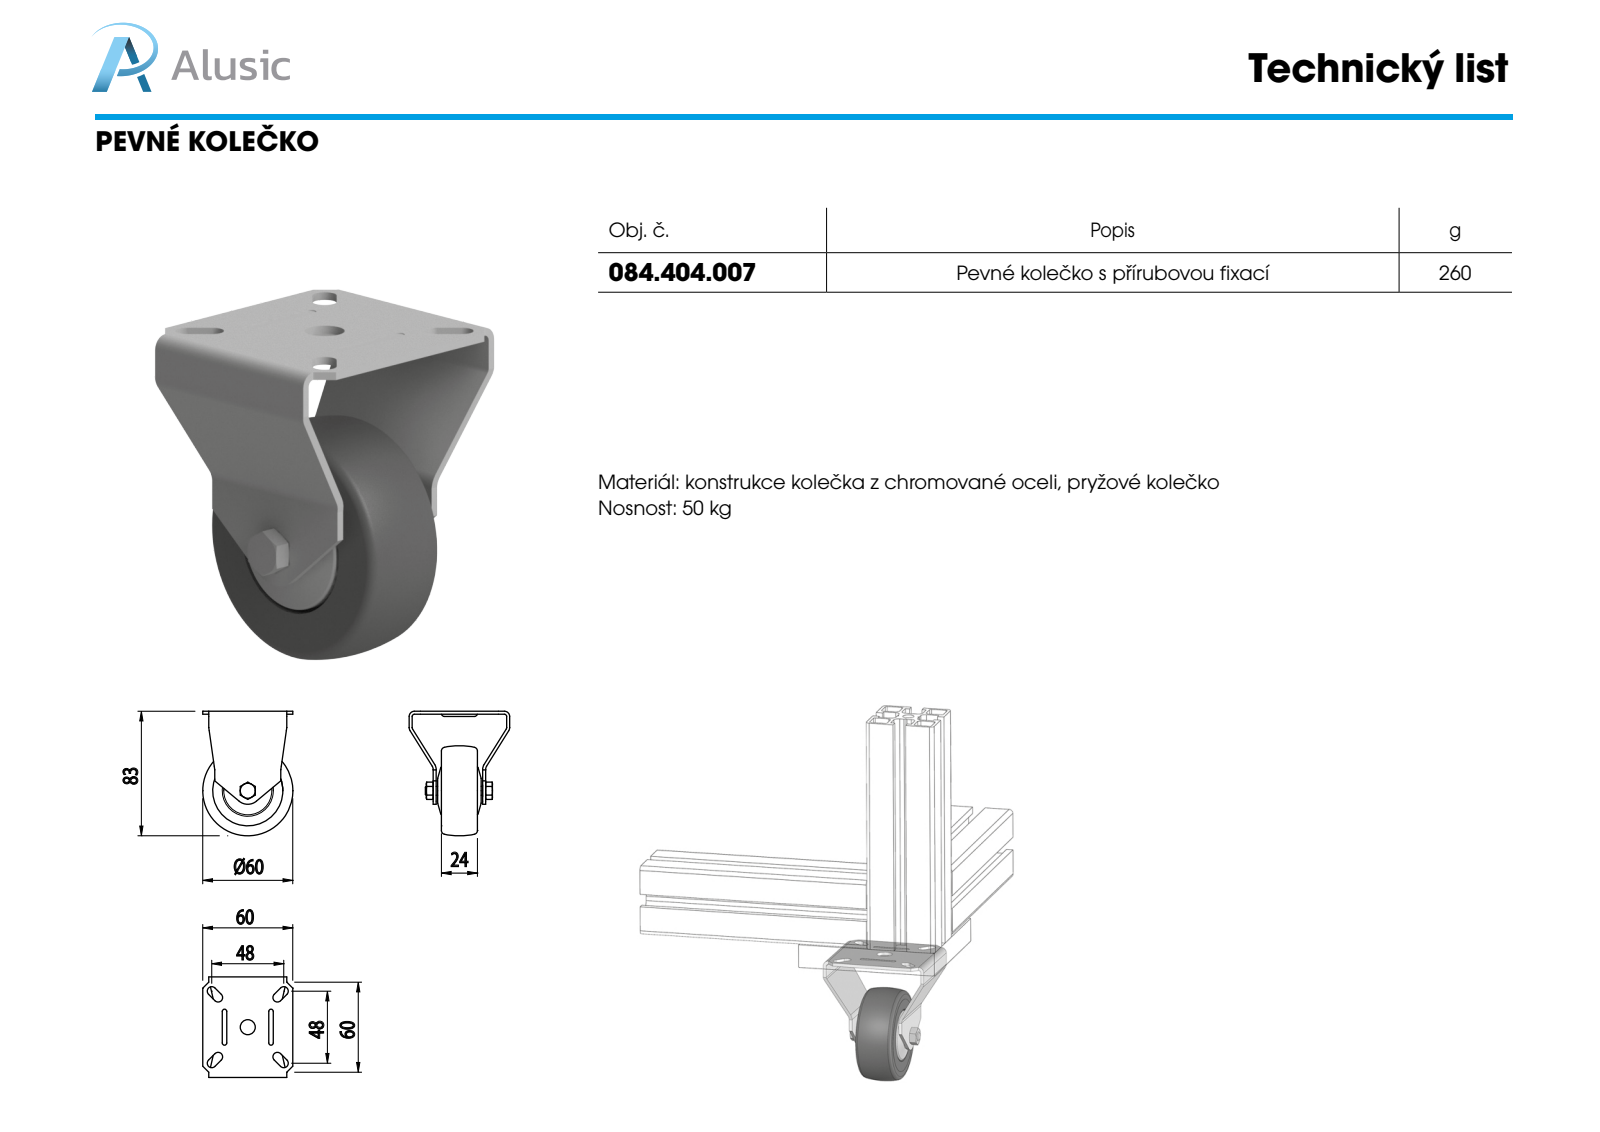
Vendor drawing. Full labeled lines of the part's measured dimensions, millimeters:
Part name (STEP PRODUCT): 084.404.007
STEP written by: SolidWorks 2011 (CONFIG_CONTROL_DESIGN)
Units: millimetres
Bodies: 7 solids, 245 faces (89 planar, 76 cylindrical, 80 other)
Overall size (bounding box): 82.98 × 67 × 60
Volume: 74 547 mm³ · Surface area: 38 800 mm²
Round holes (diameter × count): ⌀4.92 ×1, ⌀6 ×1, ⌀8 ×1, ⌀10 ×1, ⌀31 ×1, ⌀34 ×1, ⌀46.74 ×1
Round bosses / shafts (diameter × count): ⌀46.7 ×1, ⌀32 ×1, ⌀7.9 ×1, ⌀5.9 ×1
Partial cylindrical surfaces — rounded edges, fillets, slot ends (radius × count): R3 ×8, R1.5 ×6, R4 ×4, R2 ×2, R3.5 ×2, R6 ×2, R9 ×1
Main face-to-face distances: 2, 29.5, 3.5, 16, 19.5, 49, 5.5, 24, 33, 27.5
